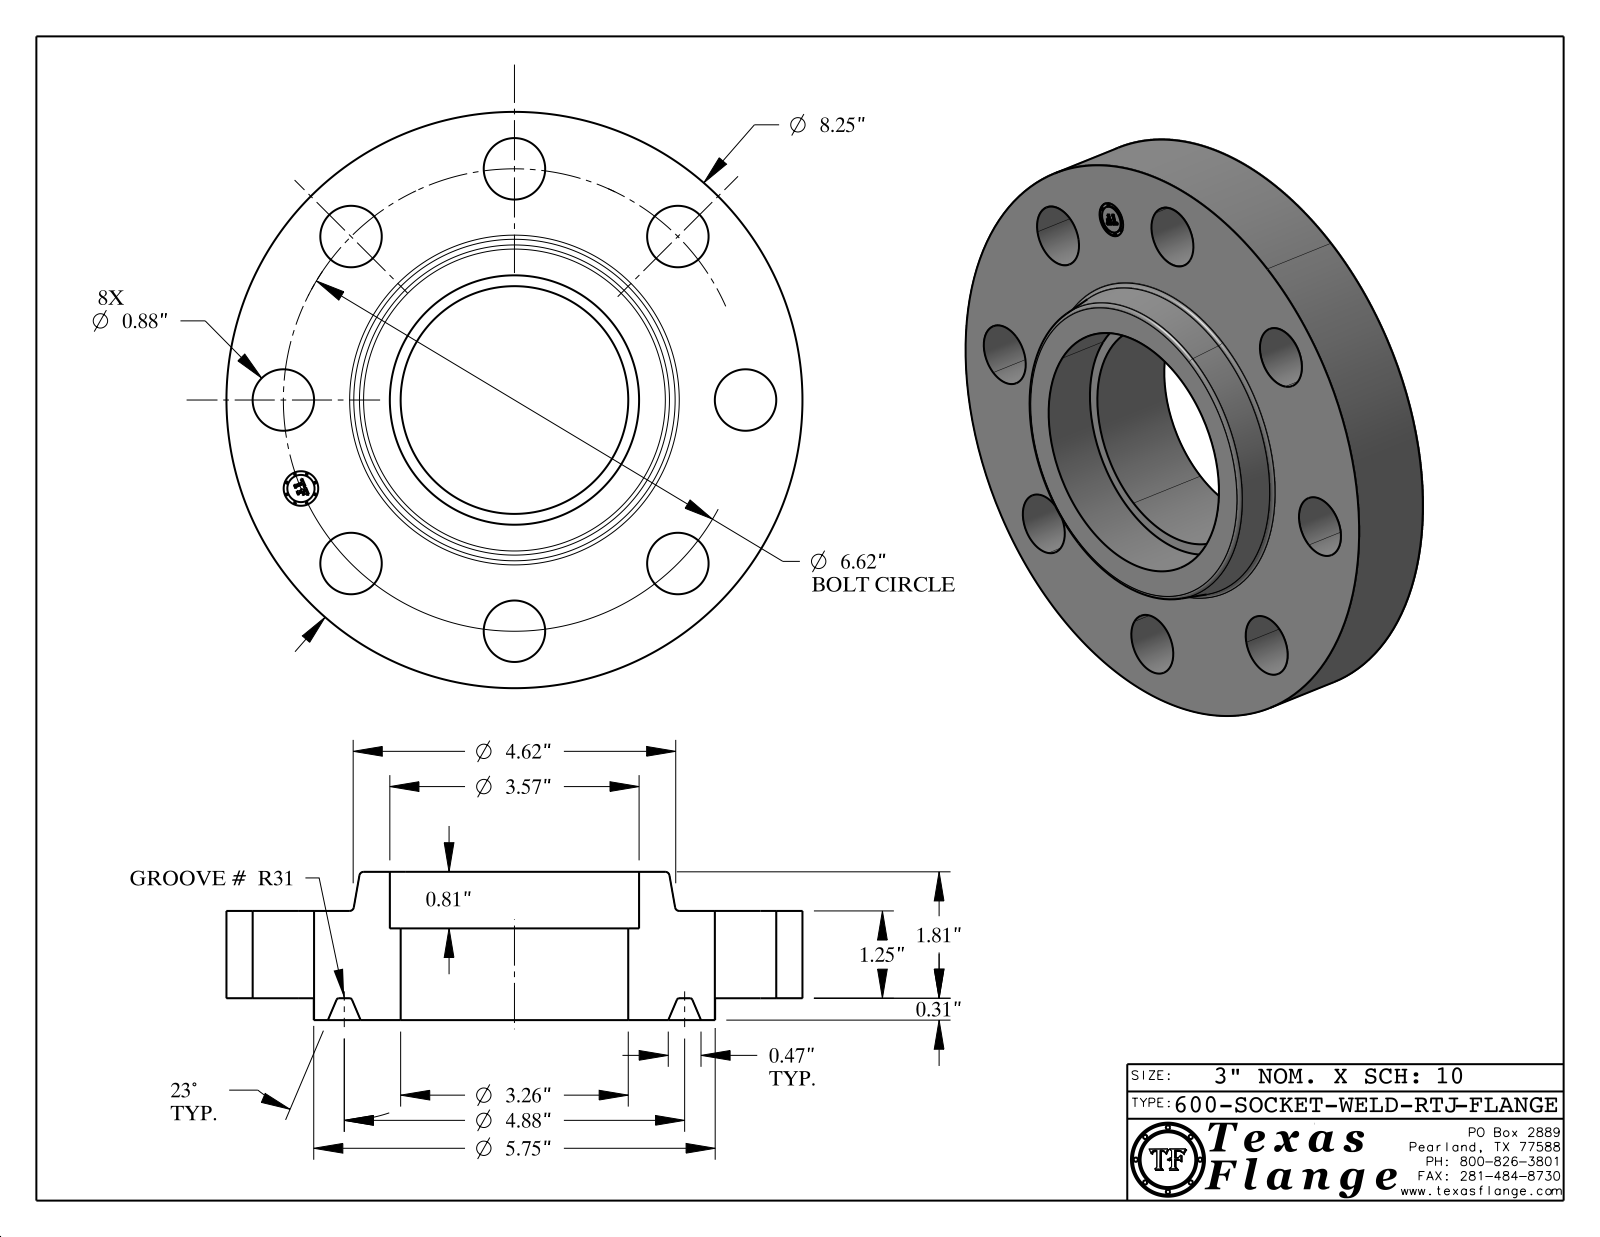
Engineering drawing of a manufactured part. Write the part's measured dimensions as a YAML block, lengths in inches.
part_name: "600-SOCKET-WELD-RTJ"
step_written_by: "CATIA V5 STEP AP214 (AUTOMOTIVE_DESIGN)"
units: inches
bodies: {solids: 1, faces: 438, planar: 372, cylindrical: 52, other: 14}
overall_size: [8.25, 8.25, 2.123]
volume: 57.18
surface_area: 181.2
round_holes:
  - {diameter: 0.88, count: 8}
  - {diameter: 0.495, count: 1}
  - {diameter: 3.26, count: 1}
  - {diameter: 3.57, count: 1}
round_bosses_or_shafts:
  - {diameter: 0.03, count: 8}
  - {diameter: 8.25, count: 1}
  - {diameter: 5.75, count: 1}
  - {diameter: 0.39, count: 1}
face_to_face_distances: [1.25, 0.313, 1.563, 2.123, 1.81, 0.56, 1.313, 1, 0.25, 0.81]
hole_center_spacings: [3.31, 2.533, 6.116, 4.681, 4.681, 1.291, 3.678, 6.493]
